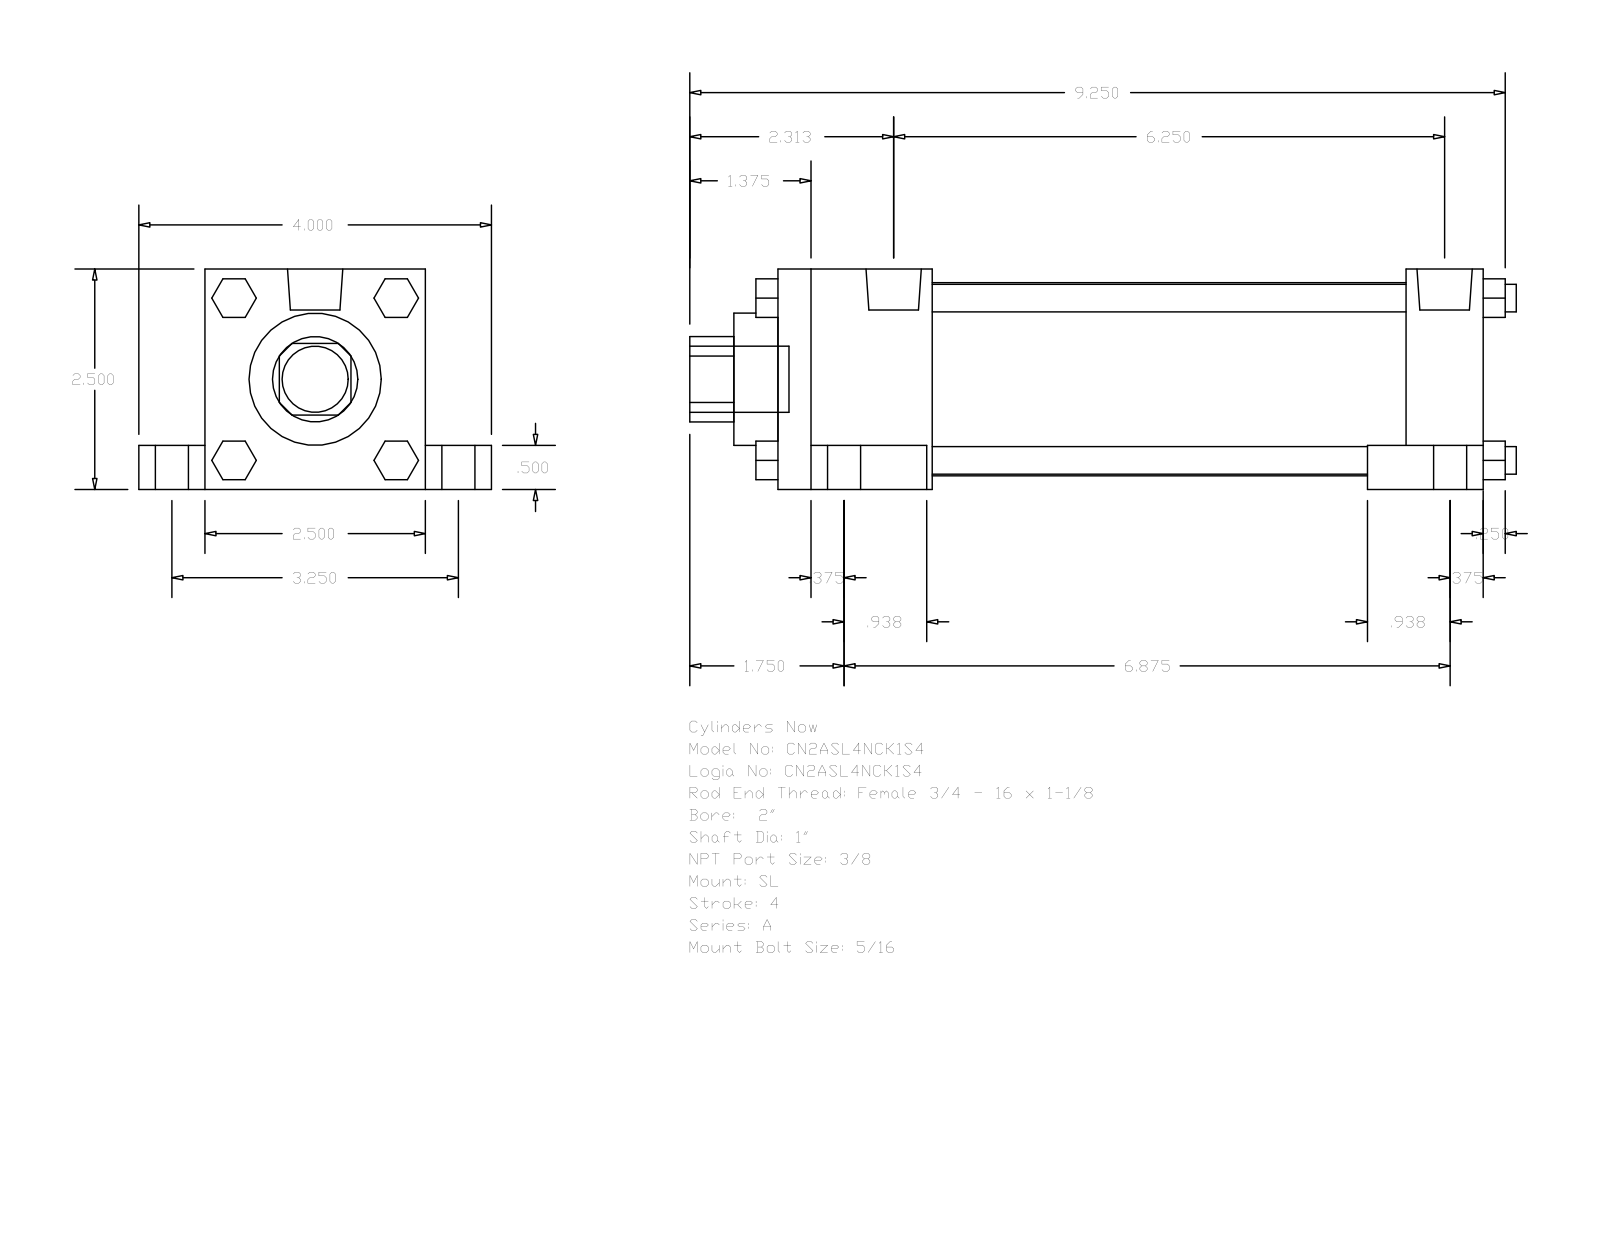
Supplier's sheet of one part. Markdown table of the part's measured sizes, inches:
| quantity | value |
| --- | --- |
| part name | A_SL__0200_1 |
| STEP written by | GSSL Pune (CONFIG_CONTROL_DESIGN) |
| units | inches |
| bodies | 0 solids, 148 faces (112 planar, 36 cylindrical, 0 other) |
| overall size | 9.375 × 4 × 2.5 |
| round holes (diameter × count) | 1 × 1, 1.5 × 1, 2.19 × 1 |
| round bosses / shafts (diameter × count) | 0.625 × 4, 0.375 × 4, 0.313 × 4, 0.219 × 4, 0.627 × 2, 0.75 × 1 |
| partial cylindrical surfaces (radius × count) | 0.484 × 1 |
| main face-to-face distances | 2.5, 8, 0.5, 2, 0.875, 0.75, 3.25, 0.375, 1.75, 6.25 |
